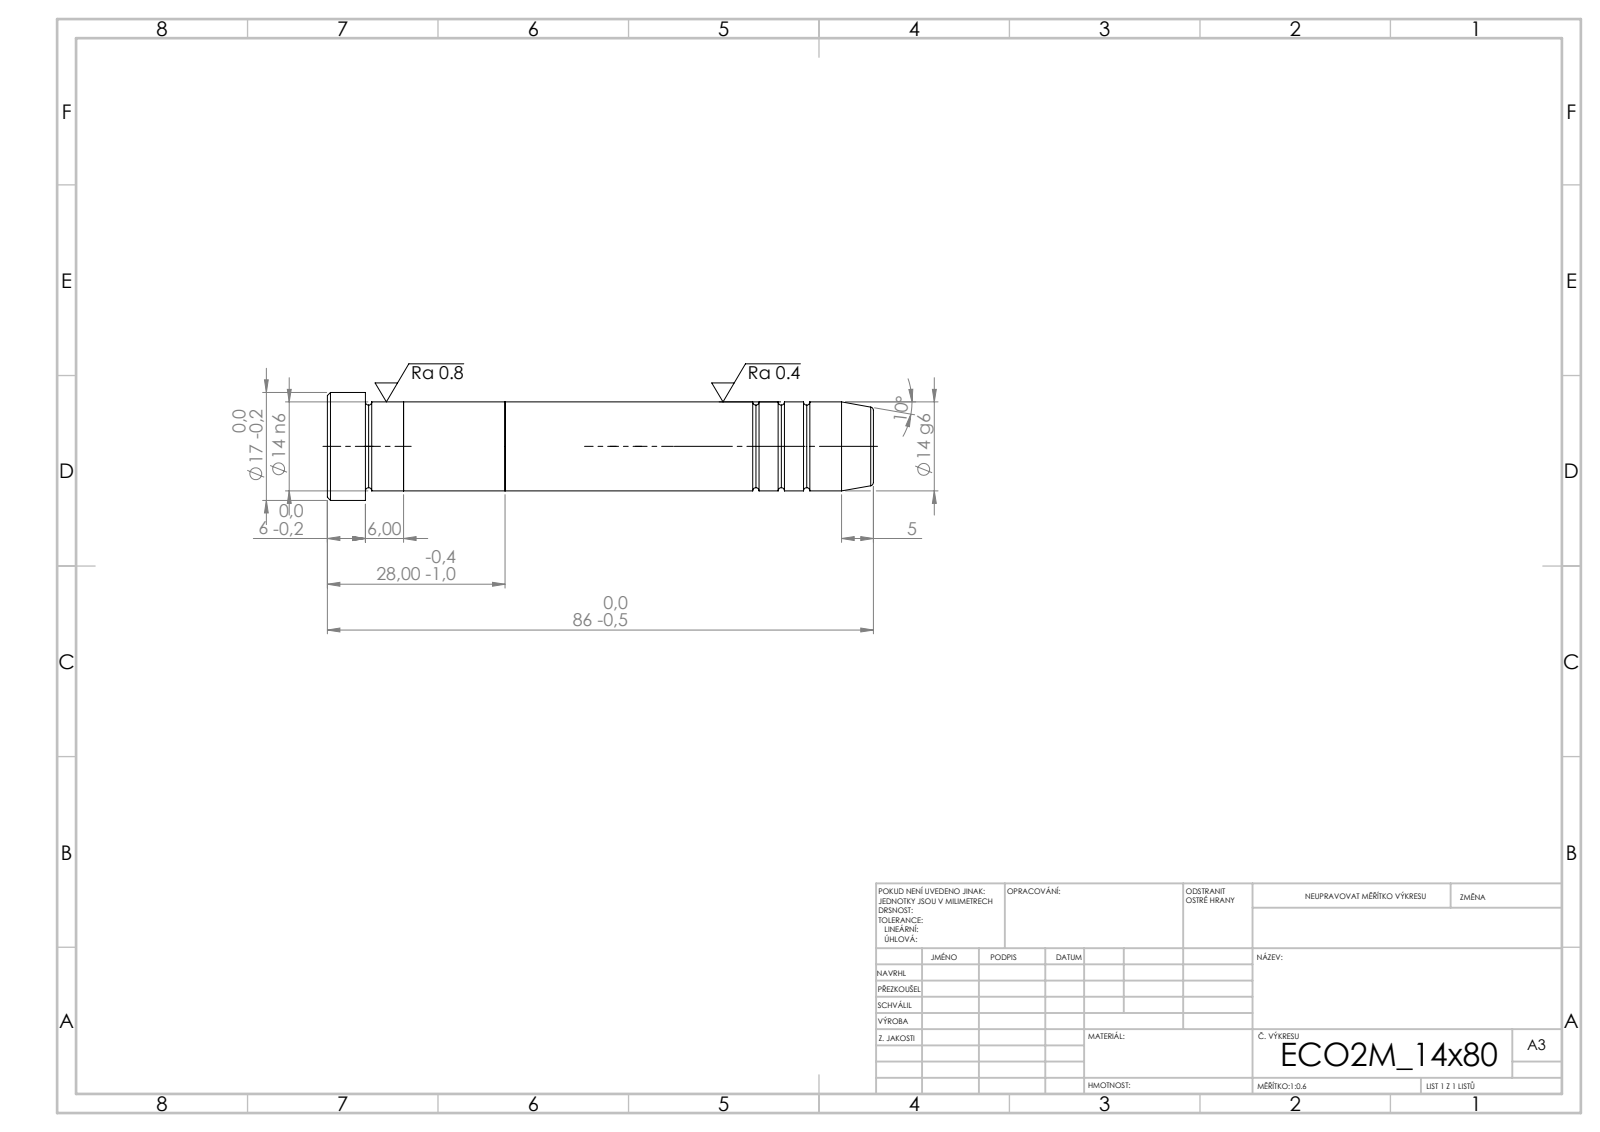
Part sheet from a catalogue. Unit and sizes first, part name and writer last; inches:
Units: inches
Overall size (bounding box): 3.386 × 0.669 × 0.669
Round bosses / shafts (diameter × count): ⌀0.669 ×1, ⌀0.551 ×1
Main face-to-face distances: 0.63, 1.102, 0.472, 0.236, 2.283, 2.913, 3.386, 3.15, 0.866
Volume: 0.824 in³ · Surface area: 7.638 in²
Bodies: 3 solids, 43 faces (7 planar, 14 cylindrical, 22 other)
STEP written by: SolidWorks 2019 (CONFIG_CONTROL_DESIGN)
